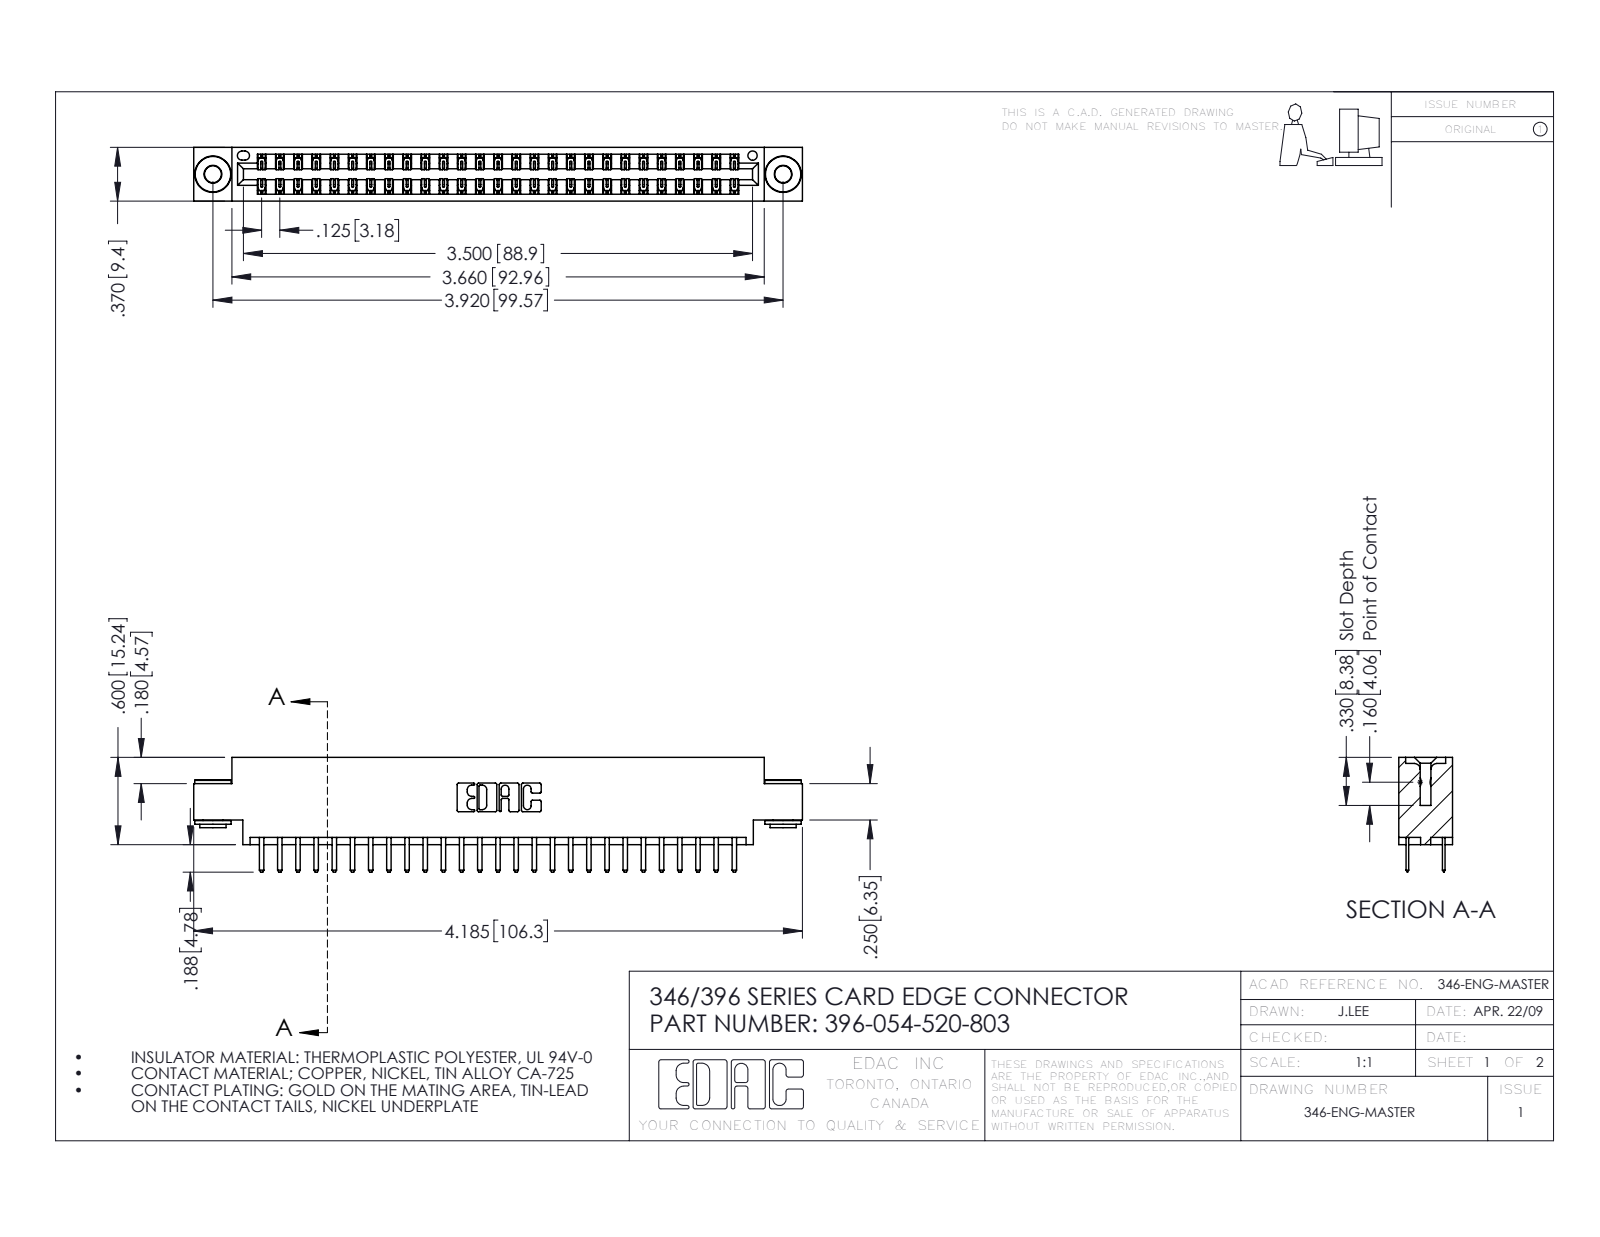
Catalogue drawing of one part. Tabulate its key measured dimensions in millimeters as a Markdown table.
| quantity | value |
| --- | --- |
| part name | 346 Part_0.170 Offset - 0.156 Dia-TH; 345-250-002_345-250-002-102; 396-054-520-803; 345-292-001_345-293-120 |
| STEP written by | SolidWorks 2016 (CONFIG_CONTROL_DESIGN) |
| units | millimeters |
| bodies | 57 solids, 3188 faces (2088 planar, 1092 cylindrical, 8 other) |
| overall size | 106.3 × 20 × 9.4 |
| volume | 10 100 mm³ |
| surface area | 13 970 mm² |
| round holes (diameter × count) | 2.9 × 2, 4 × 2, 1.6 × 1 |
| round bosses / shafts (diameter × count) | 6.4 × 2, 4.6 × 2, 3.5 × 2 |
| partial cylindrical surfaces (radius × count) | 0.2 × 81, 0.3 × 58, 0.3 × 22, 0.2 × 6, 0.8 × 6, 0.7 × 3, 0.4 × 2, 0.6 × 2 |
| main face-to-face distances | 1.2, 8.2, 6.4, 9.4, 0.6, 7, 1.8, 7.6, 3.8, 5.6 |
| hole center spacings | 6.2, 94.3, 99.6 |
